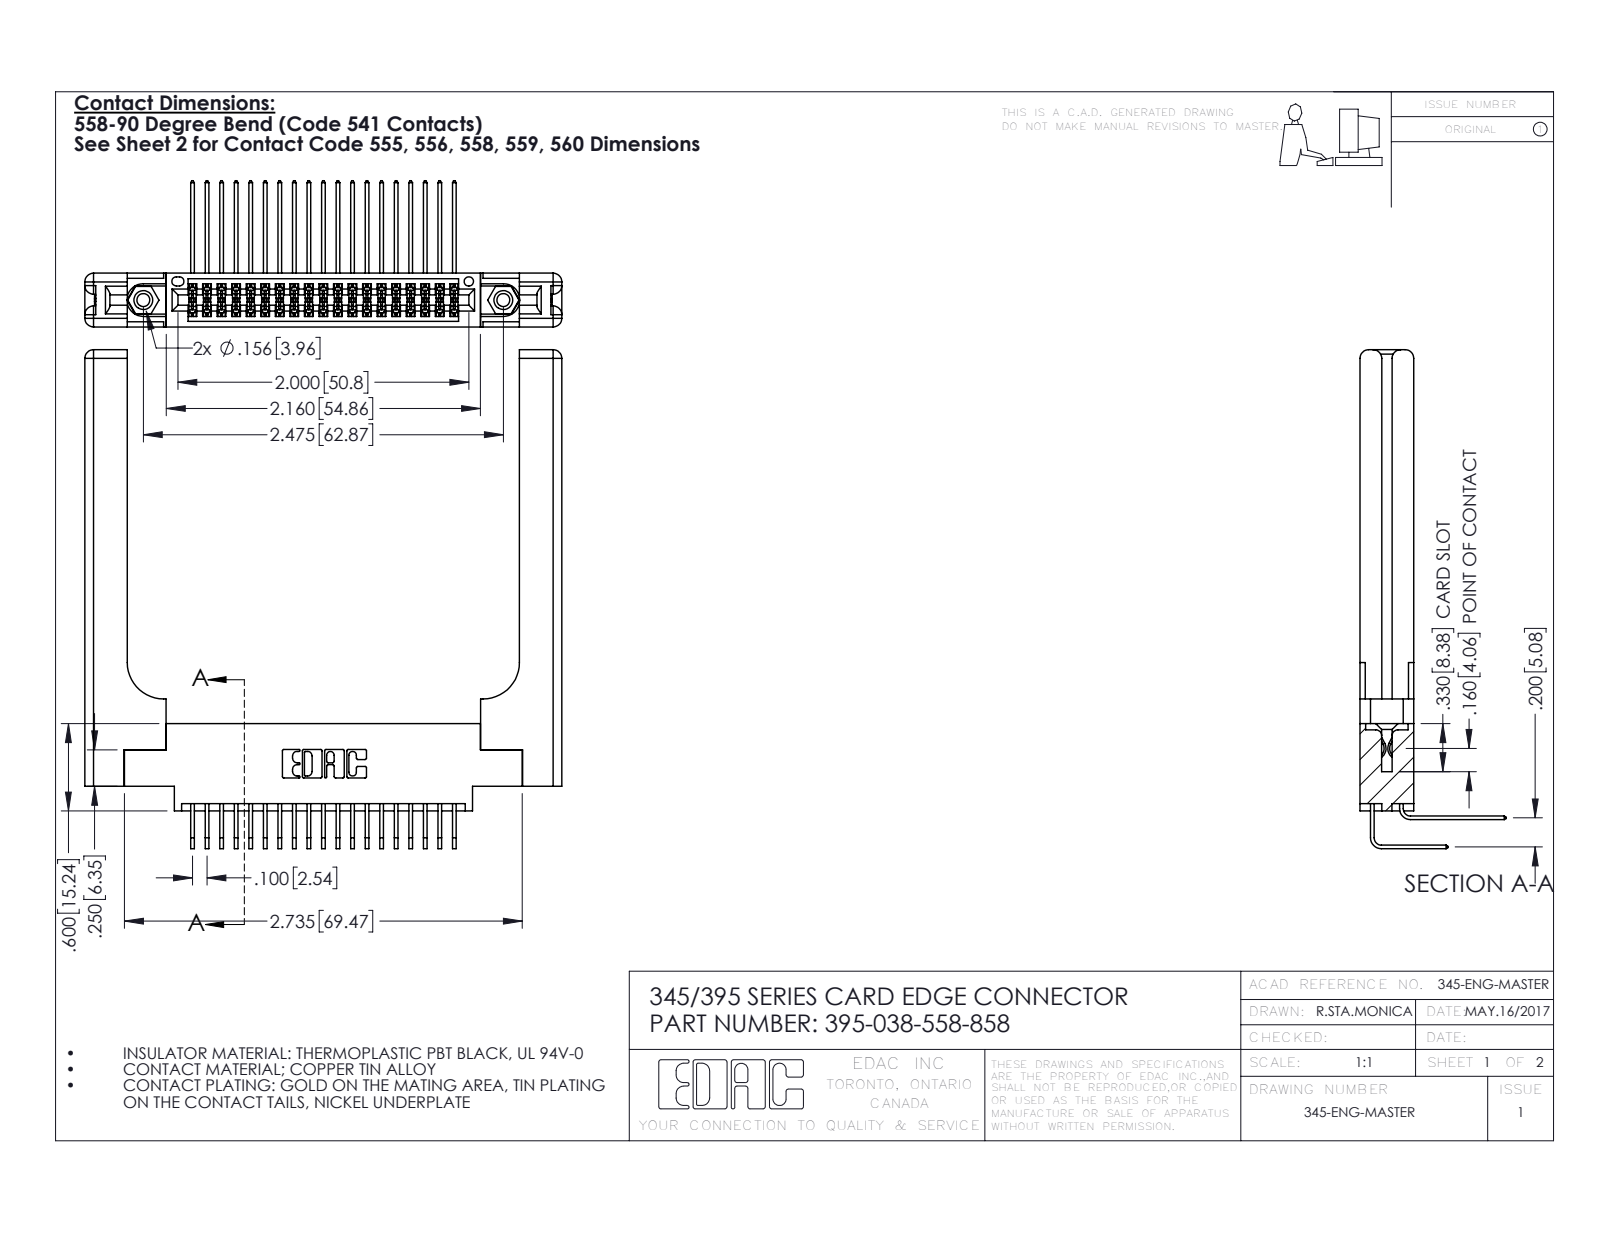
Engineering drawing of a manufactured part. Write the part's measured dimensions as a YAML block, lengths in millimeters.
part_name: "345-292-001_558 Tail - 2; 345-292-001_558 559 Tail - 1; 345-220-058_345-220-058; 345 Part_0.170 Offset - 0.156 Dia-TH (+2 more)"
step_written_by: "SolidWorks 2016 (CONFIG_CONTROL_DESIGN)"
units: millimeters
bodies: {solids: 43, faces: 2362, planar: 1562, cylindrical: 740, other: 60}
overall_size: [87.1, 83.3, 25.5]
volume: 16450
surface_area: 17590
round_holes:
  - {diameter: 2.3, count: 2}
  - {diameter: 3.2, count: 2}
  - {diameter: 4, count: 2}
  - {diameter: 1.6, count: 1}
round_bosses_or_shafts:
  - {diameter: 3.9, count: 2}
partial_cylinders:
  - {radius: 0.2, count: 58}
  - {radius: 0.3, count: 22}
  - {radius: 1.5, count: 16}
  - {radius: 0.2, count: 6}
  - {radius: 0.8, count: 6}
  - {radius: 0.7, count: 3}
  - {radius: 0.4, count: 2}
  - {radius: 0.5, count: 2}
face_to_face_distances: [9.4, 1.8, 7.6, 5.1, 3.8, 3.8, 2, 5.6, 2.5, 6.9]
hole_center_spacings: [6.9, 56.9, 62.9]
